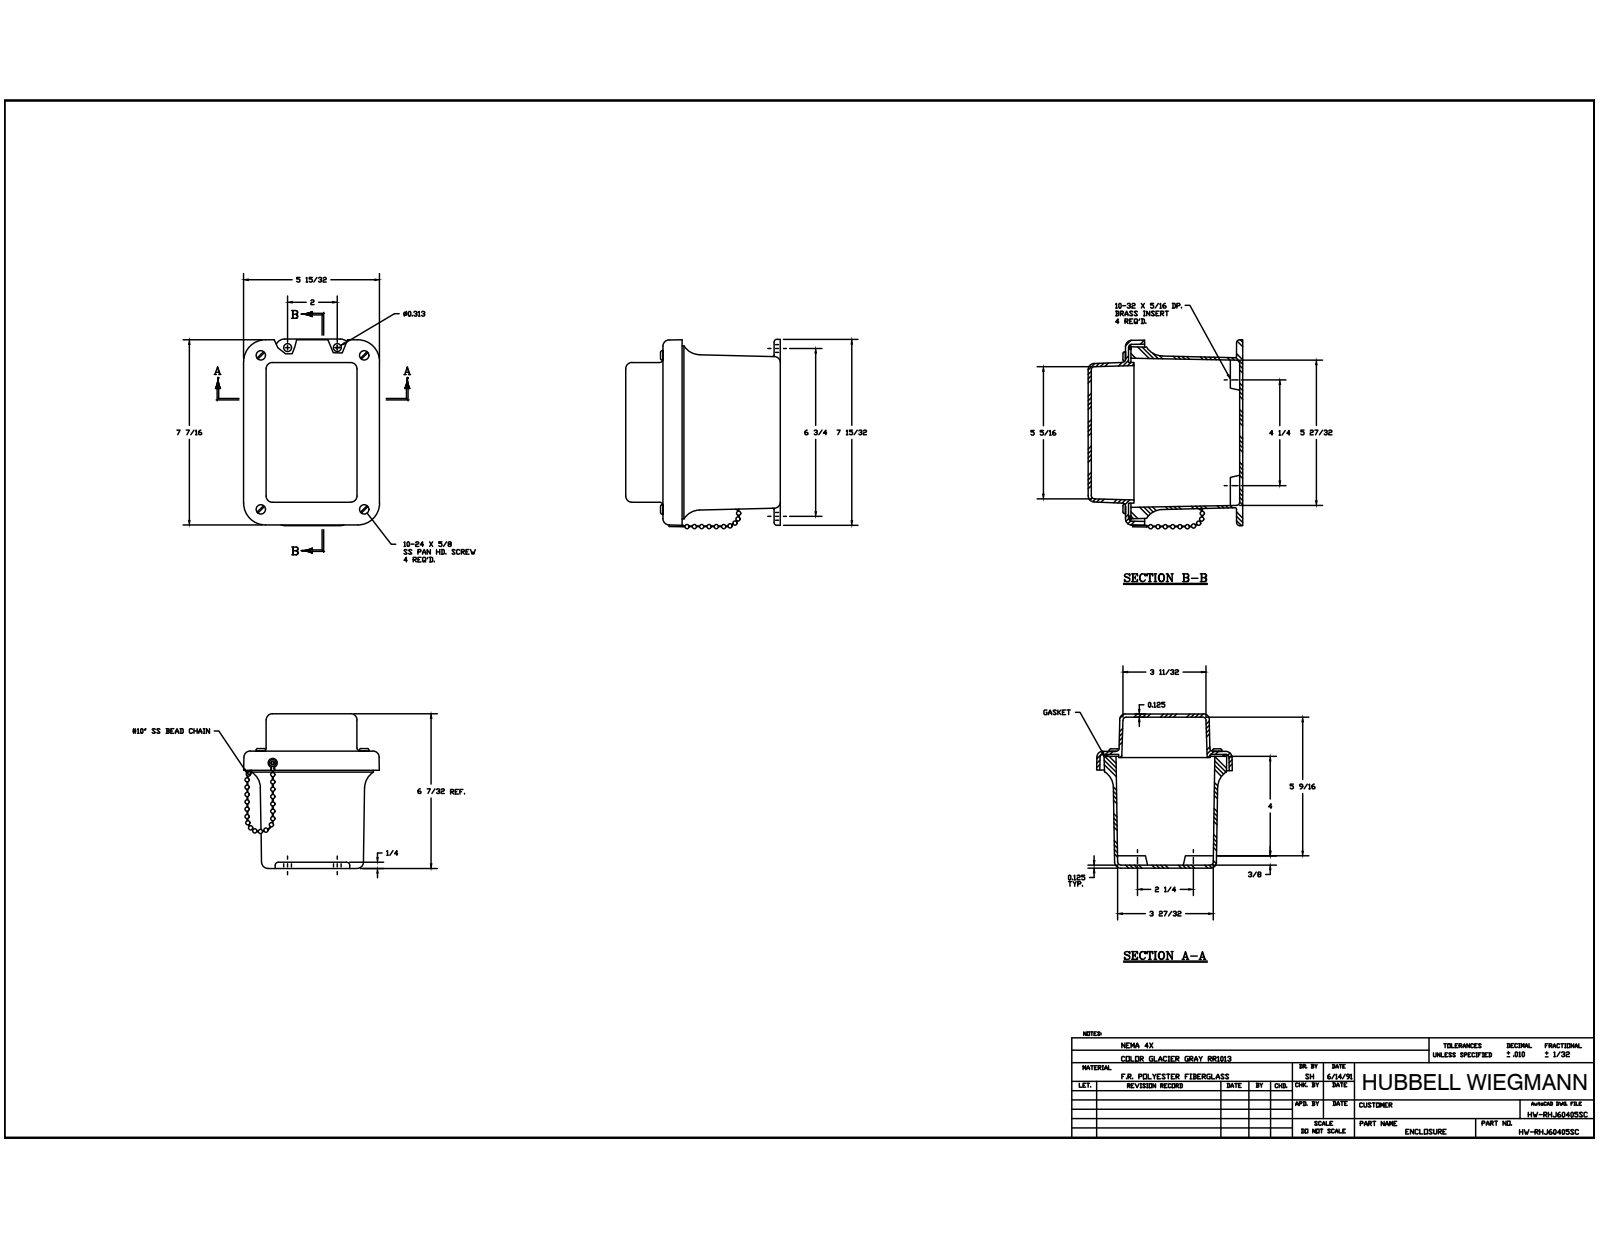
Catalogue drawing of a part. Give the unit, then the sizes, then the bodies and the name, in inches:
Units: inches
Overall size (bounding box): 8.072 × 6.213 × 5.797
Round holes (diameter × count): ⌀0.152 ×5, ⌀0.145 ×4, ⌀0.156 ×4, ⌀0.218 ×4, ⌀0.14 ×3, ⌀0.187 ×2, ⌀0.126 ×1
Round bosses / shafts (diameter × count): ⌀0.27 ×8, ⌀0.19 ×4, ⌀0.156 ×4, ⌀0.375 ×2, ⌀0.25 ×2, ⌀0.125 ×2, ⌀0.283 ×1
Partial cylindrical surfaces — rounded edges, fillets, slot ends (radius × count): R0.031 ×20, R0.125 ×20, R0.25 ×12, R0.2 ×4, R0.309 ×4, R0.313 ×4, R0.375 ×4, R0.75 ×4
Main face-to-face distances: 0.125, 0.125, 1.5, 4.463, 4.588, 5.963, 6.088, 6.213, 1.625, 6.088
Hole centre spacings: 3.339, 1.341, 2.25, 4.156, 4.25, 4.808, 5.28, 6.102
Volume: 33.28 in³ · Surface area: 436.8 in²
Bodies: 21 solids, 913 faces (208 planar, 297 cylindrical, 408 other)
Part name (STEP PRODUCT): J604W_3; RMINS45821P_45; RMINS45821P_46; RMINS45821P_47 (+8 more)
STEP written by: Autodesk Inventor 2014 (AUTOMOTIVE_DESIGN)
